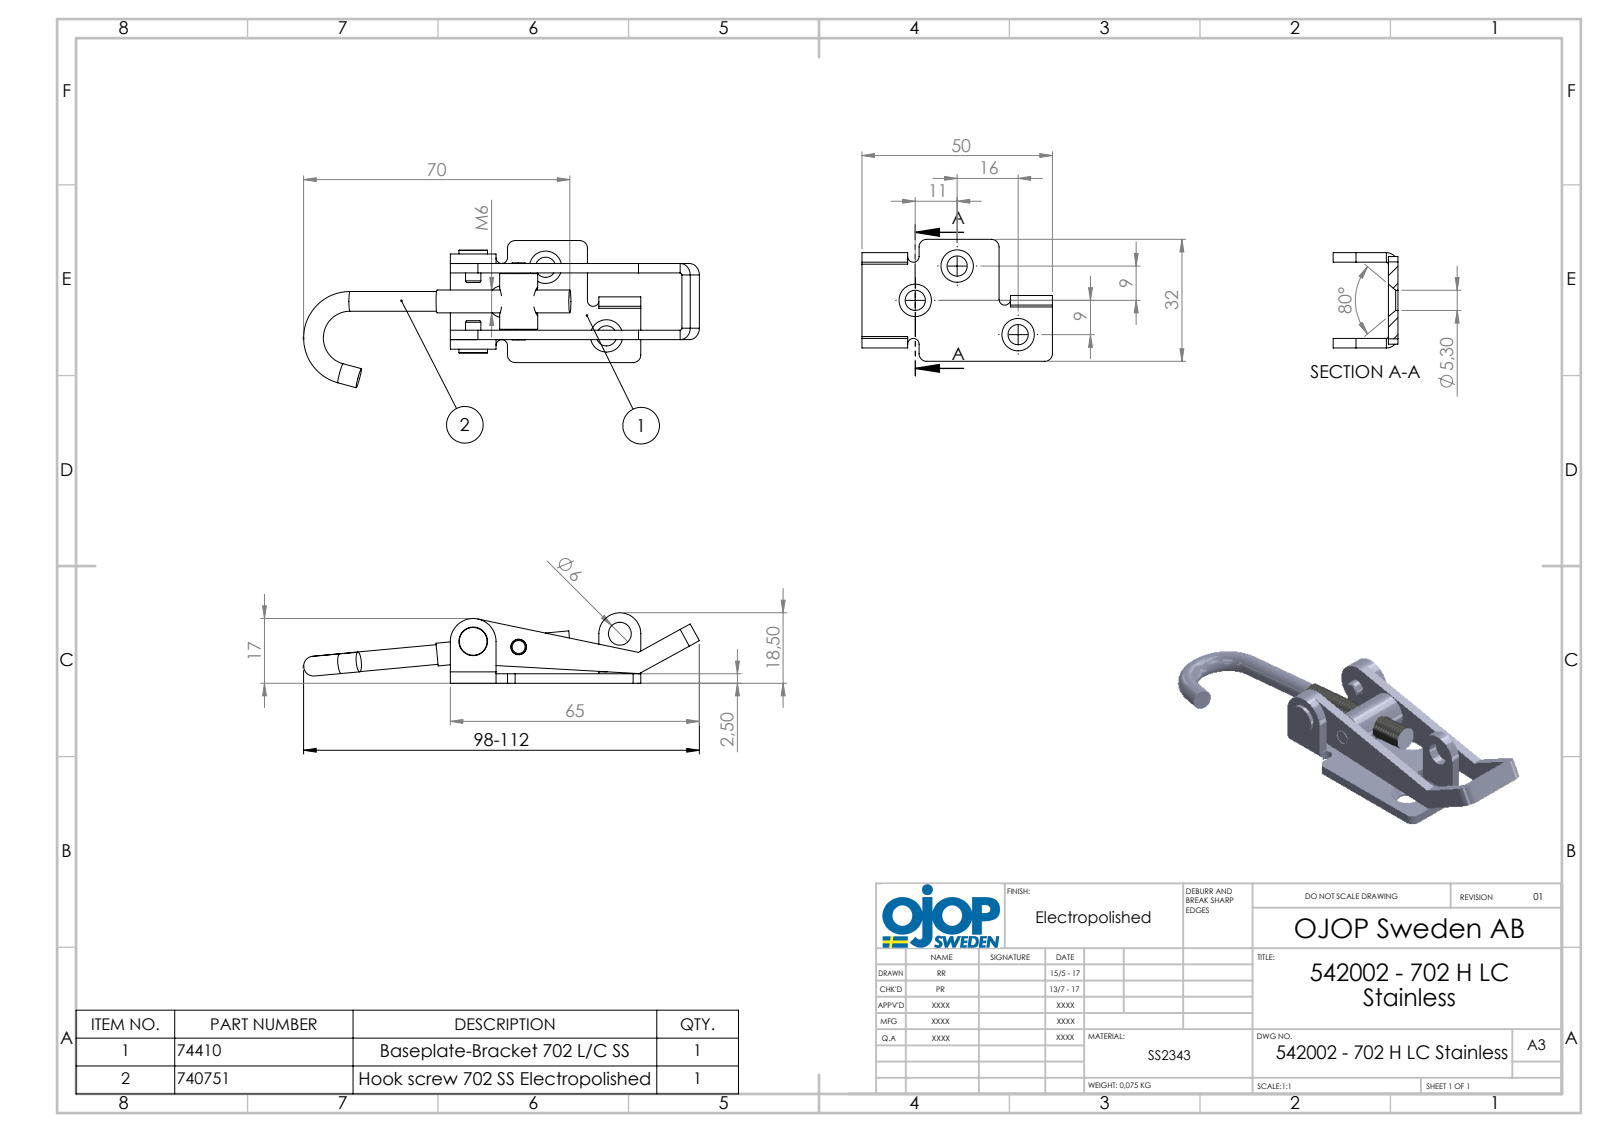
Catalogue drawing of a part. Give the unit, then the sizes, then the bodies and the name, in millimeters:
Units: millimetres
Overall size (bounding box): 105.32 × 38.54 × 18.5
Round holes (diameter × count): ⌀5.3 ×3, ⌀4.1 ×2, ⌀6 ×2, ⌀5 ×1
Round bosses / shafts (diameter × count): ⌀5.18 ×2, ⌀4 ×2, ⌀10 ×1, ⌀7.5 ×1, ⌀6 ×1
Partial cylindrical surfaces — rounded edges, fillets, slot ends (radius × count): R0.5 ×5, R3 ×5, R2 ×4, R1.5 ×2, R1.51 ×1, R5.5 ×1, R6 ×1
Main face-to-face distances: 2.5, 17.5, 20, 8.75, 11.25, 15, 5, 6.25, 22.5, 6
Hole centre spacings: 12.02, 14.21, 24.08, 26.8, 28.46, 38.55
Volume: 10 029 mm³ · Surface area: 9 858 mm²
Bodies: 6 solids, 159 faces (65 planar, 70 cylindrical, 24 other)
Part name (STEP PRODUCT): 702 - Hake M6; 702 - Platta LC; 702 - Bygel; 542002 - 702 H LC Stainless (+2 more)
STEP written by: SolidWorks 2015 (AUTOMOTIVE_DESIGN)
